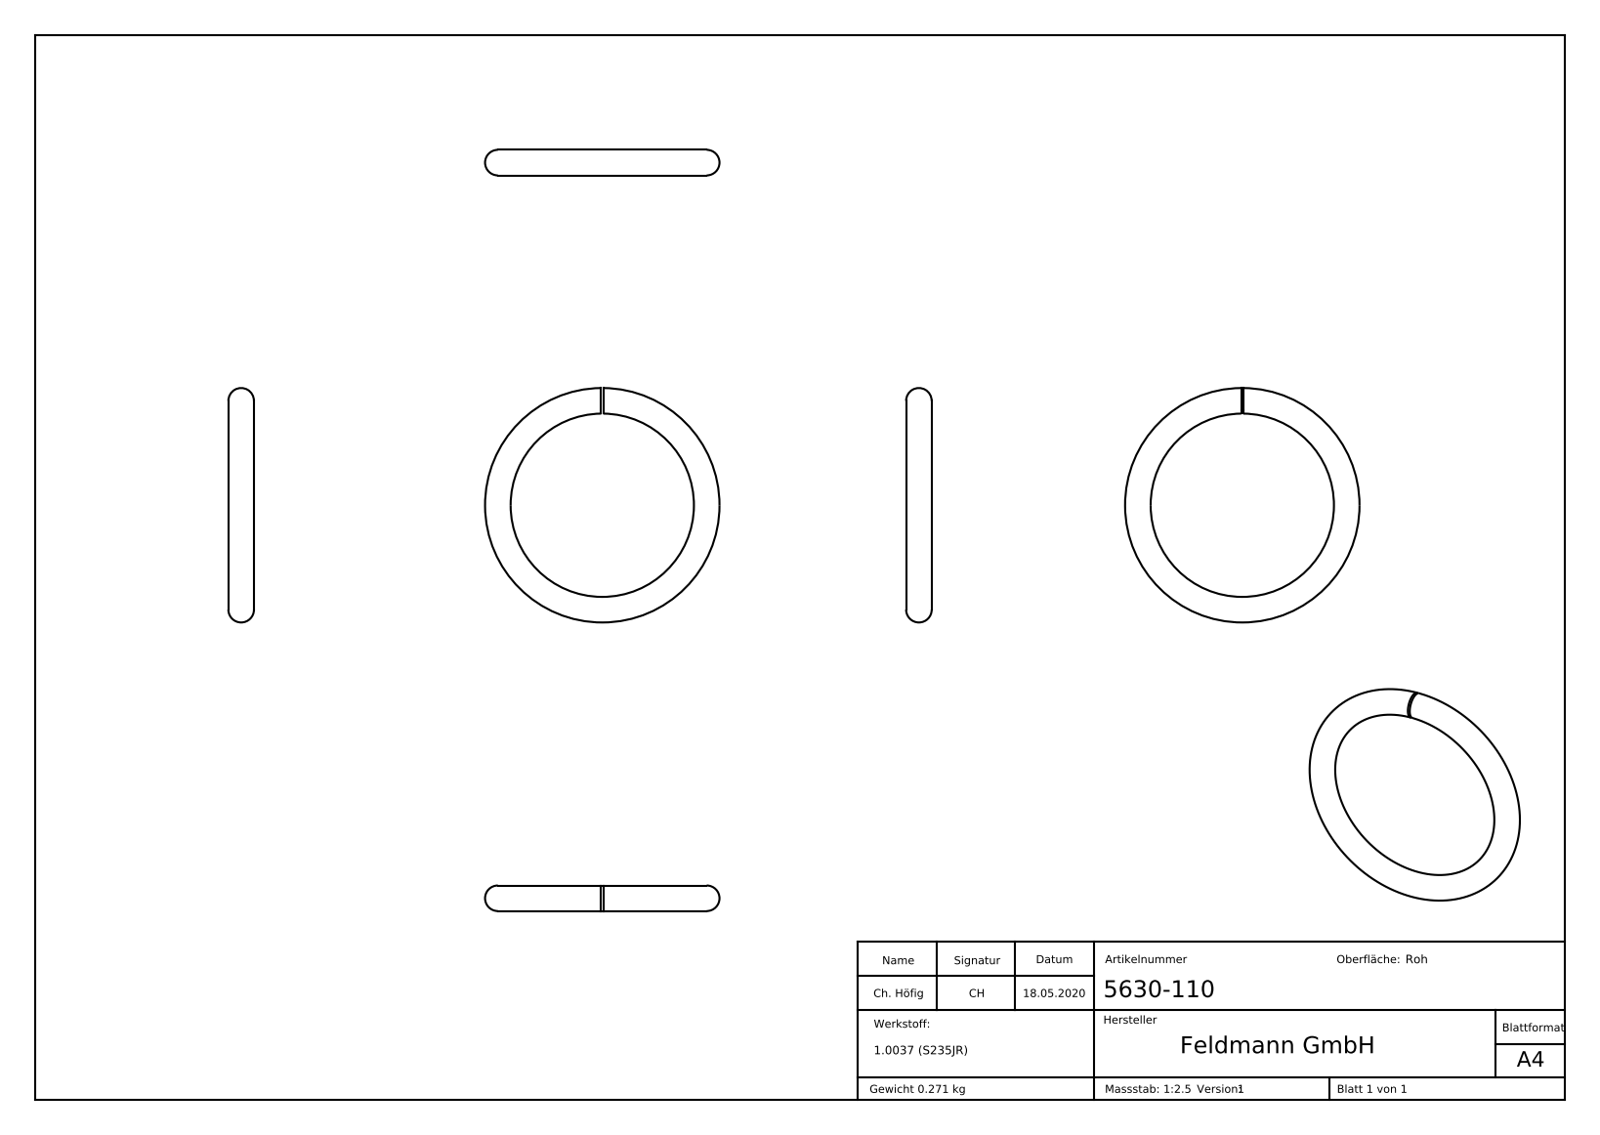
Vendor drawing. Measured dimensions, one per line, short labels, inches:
name: 5630-110
written by: SolidWorks 2015 (CONFIG_CONTROL_DESIGN)
unit: in
bodies: 1 solid, 211 faces (108 planar, 0 cylindrical, 103 other)
size: 4.331 × 4.331 × 0.472
volume: 2.117 in³; area: 18.32 in²
face distances: 0.039, 0.059, 0.02, 0.07, 0.033, 0.096, 0.083, 0.039, 0.024, 0.107
